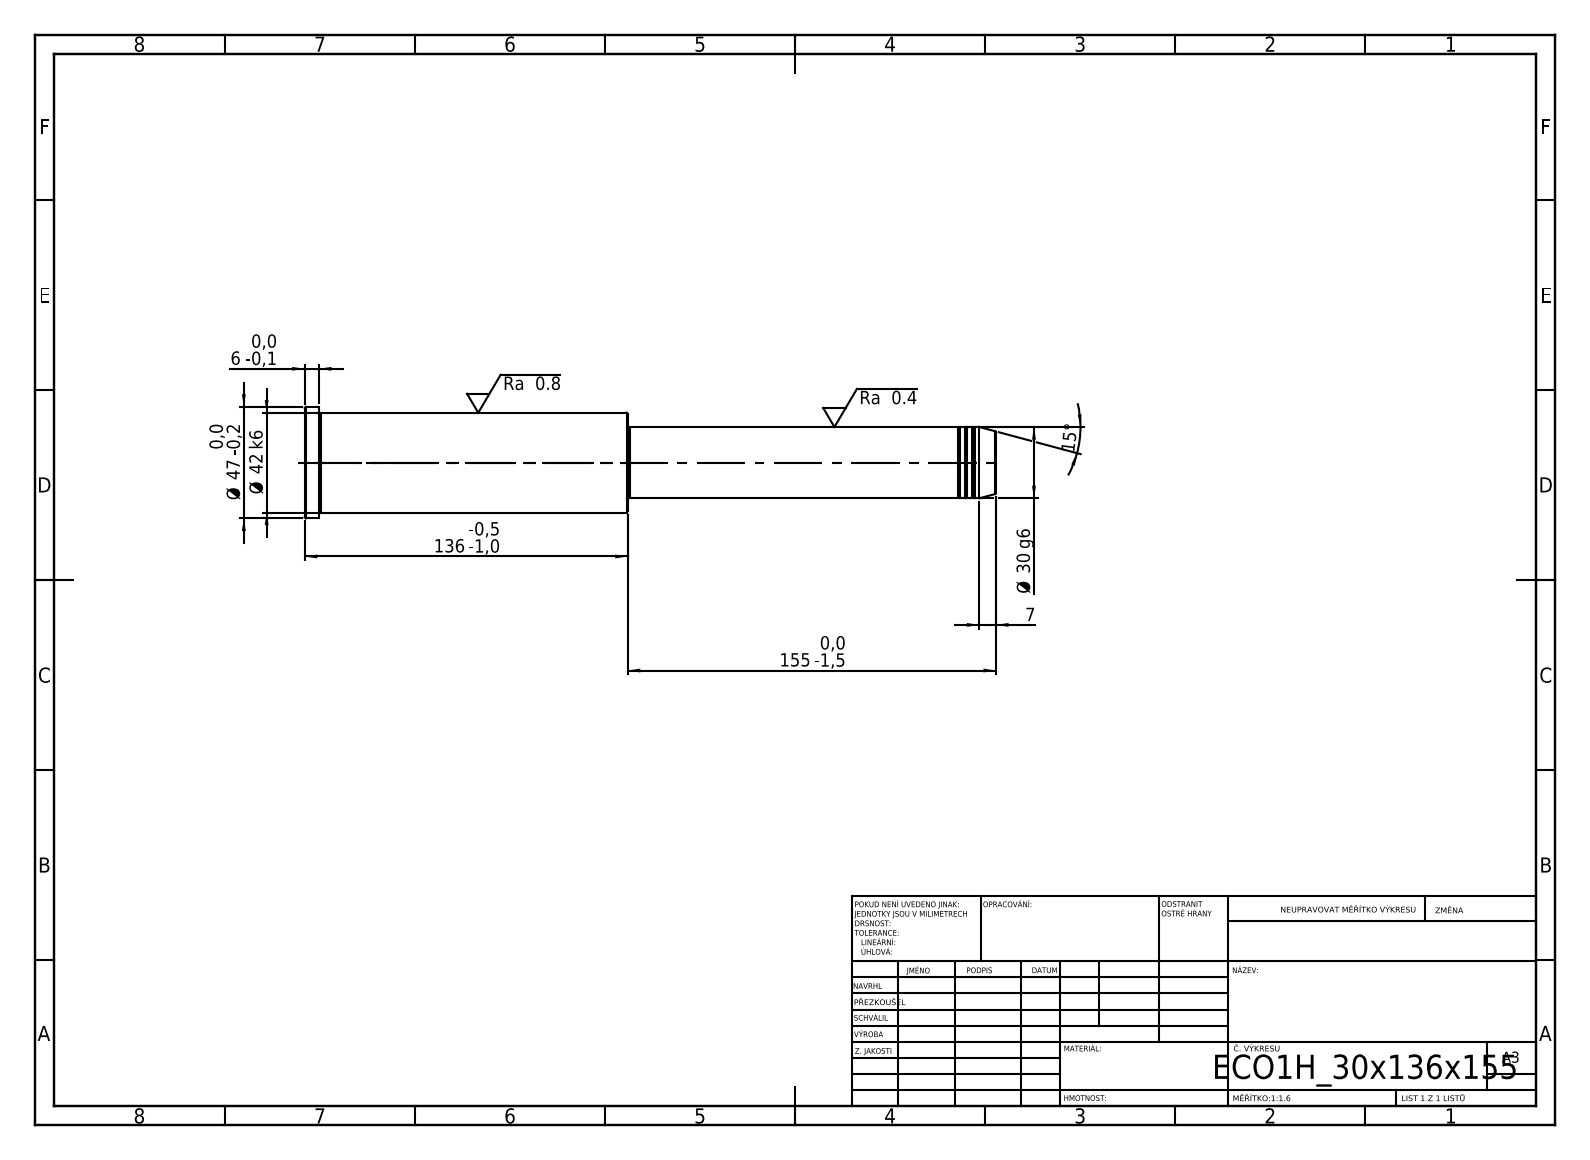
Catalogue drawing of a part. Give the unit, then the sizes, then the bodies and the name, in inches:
Units: inches
Overall size (bounding box): 11.457 × 1.85 × 1.85
Round bosses / shafts (diameter × count): ⌀1.85 ×1, ⌀1.654 ×1, ⌀1.181 ×1, ⌀1.142 ×1
Main face-to-face distances: 5.354, 6.102, 11.457, 11.22, 5.118, 0.236, 6.063, 0.039, 5.157, 5.394
Volume: 18.26 in³ · Surface area: 56.04 in²
Bodies: 1 solid, 43 faces (5 planar, 14 cylindrical, 24 other)
STEP written by: SolidWorks 2019 (CONFIG_CONTROL_DESIGN)
